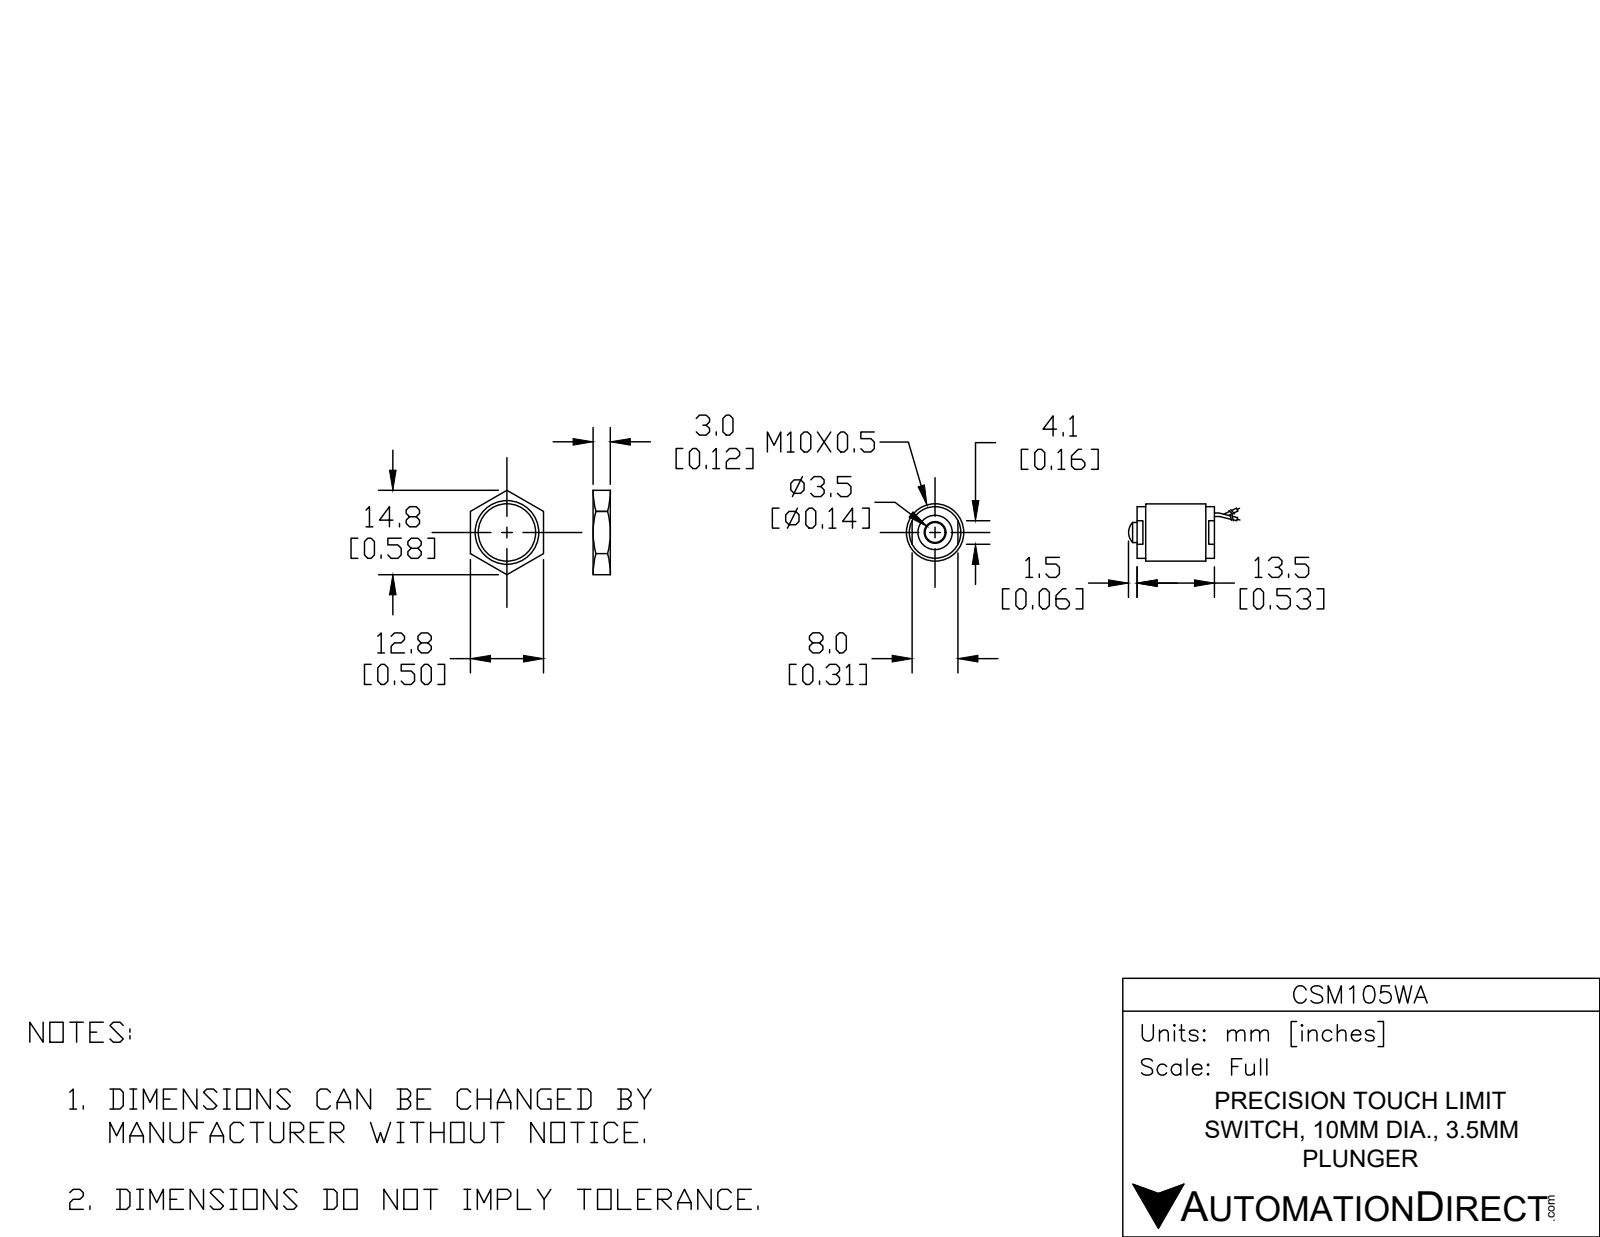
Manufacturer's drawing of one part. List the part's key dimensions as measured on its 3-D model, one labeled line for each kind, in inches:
Part name (STEP PRODUCT): CSM105WA
STEP written by: SolidWorks 2016 (CONFIG_CONTROL_DESIGN)
Units: inches
Bodies: 1 solid, 72 faces (14 planar, 53 cylindrical, 5 other)
Overall size (bounding box): 0.787 × 0.394 × 0.394
Volume: 0.059 in³ · Surface area: 1.29 in²
Round bosses / shafts (diameter × count): ⌀0.024 ×2, ⌀0.394 ×1, ⌀0.354 ×1, ⌀0.138 ×1
Main face-to-face distances: 0.531, 0.059, 0.472, 0.413, 0.315, 0.039, 0.492, 0.02, 0.433, 0.453
